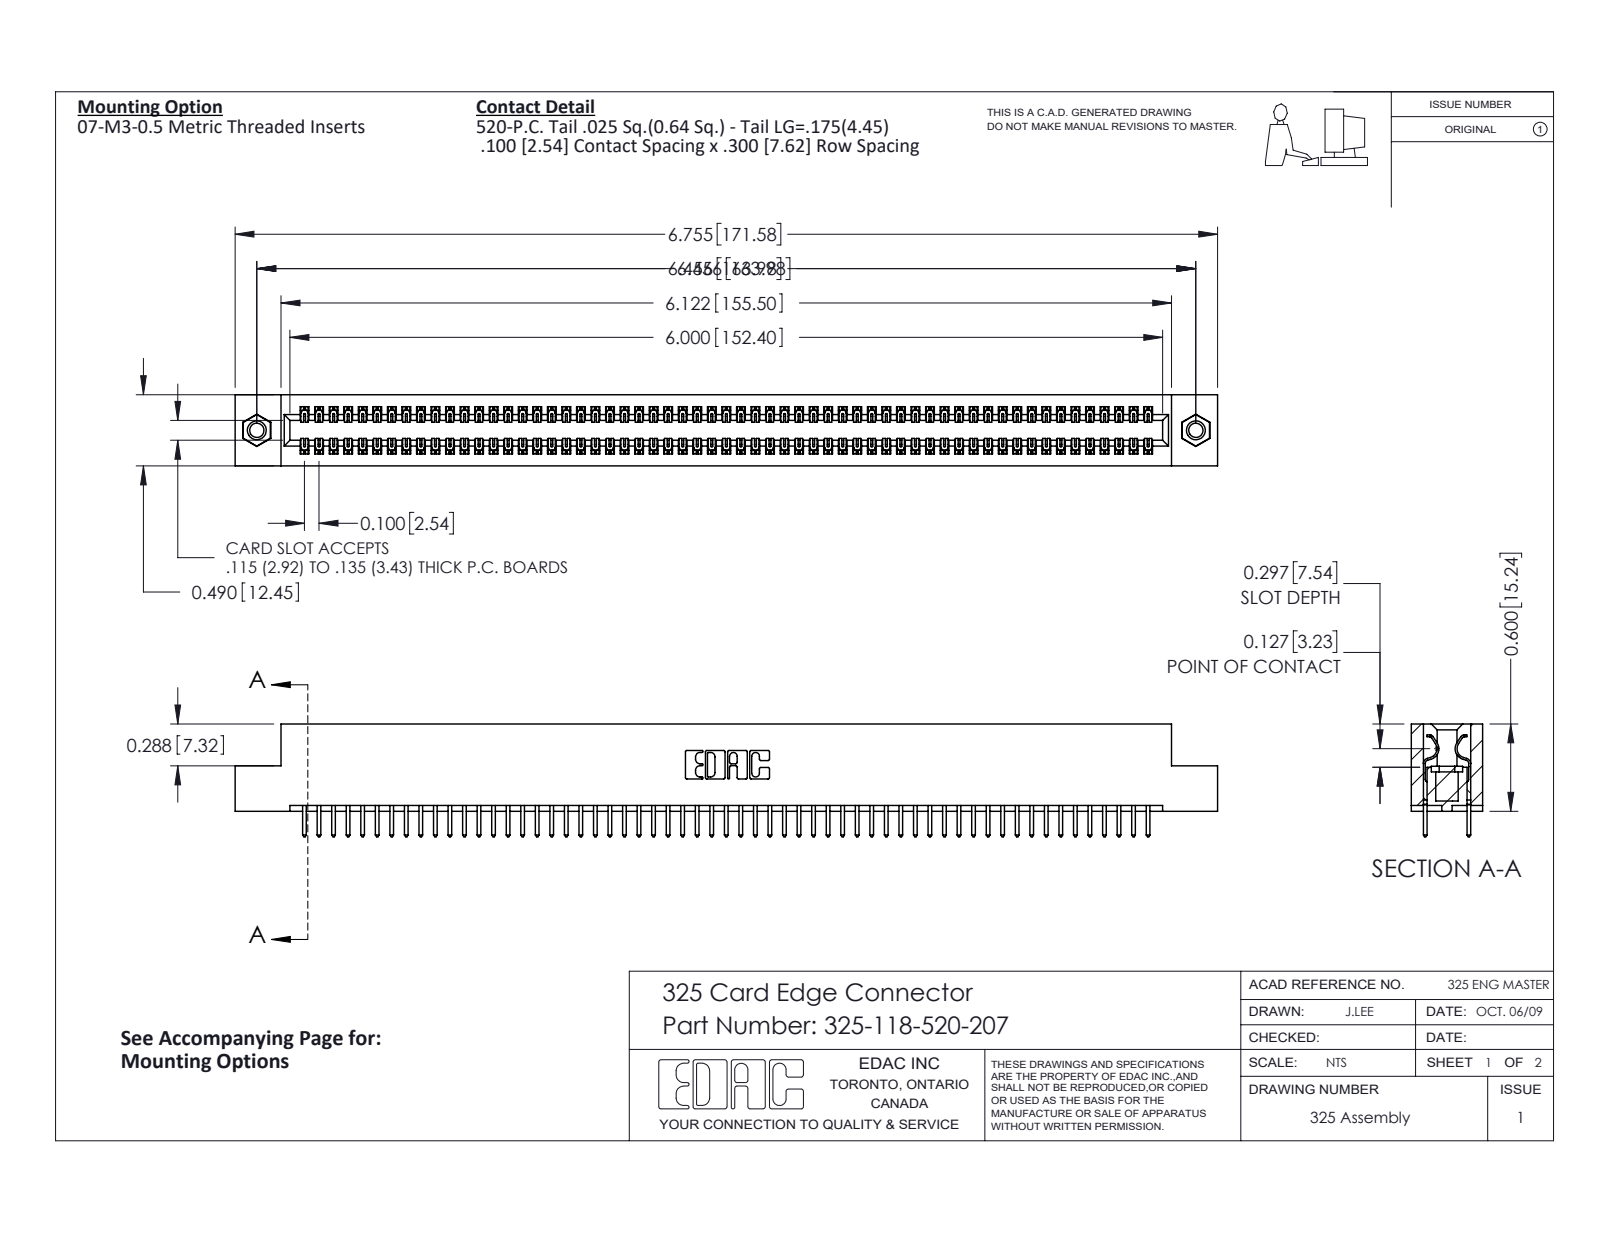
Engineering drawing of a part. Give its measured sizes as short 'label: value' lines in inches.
name: 325-118-520-207; 325-292-001_325-293-120; 325 Part_TI; 345-250-001_345-250-005-103
written by: SolidWorks 2016 (CONFIG_CONTROL_DESIGN)
unit: in
bodies: 121 solids, 6310 faces (4350 planar, 1944 cylindrical, 16 other)
size: 6.755 × 0.775 × 0.49
volume: 1.359 in³; area: 42.08 in²
holes: 2× ⌀0.098, 2× ⌀0.125, 2× ⌀0.16
bosses: 2× ⌀0.155
rounds: 177× R0.006, 118× R0.01, 22× R0.01, 6× R0.007, 6× R0.031, 3× R0.026, 2× R0.014, 2× R0.022
face distances: 0.083, 0.407, 0.3, 0.49, 0.107, 0.383, 0.025, 0.325, 0.275, 0.56
hole spacings: 6.456
